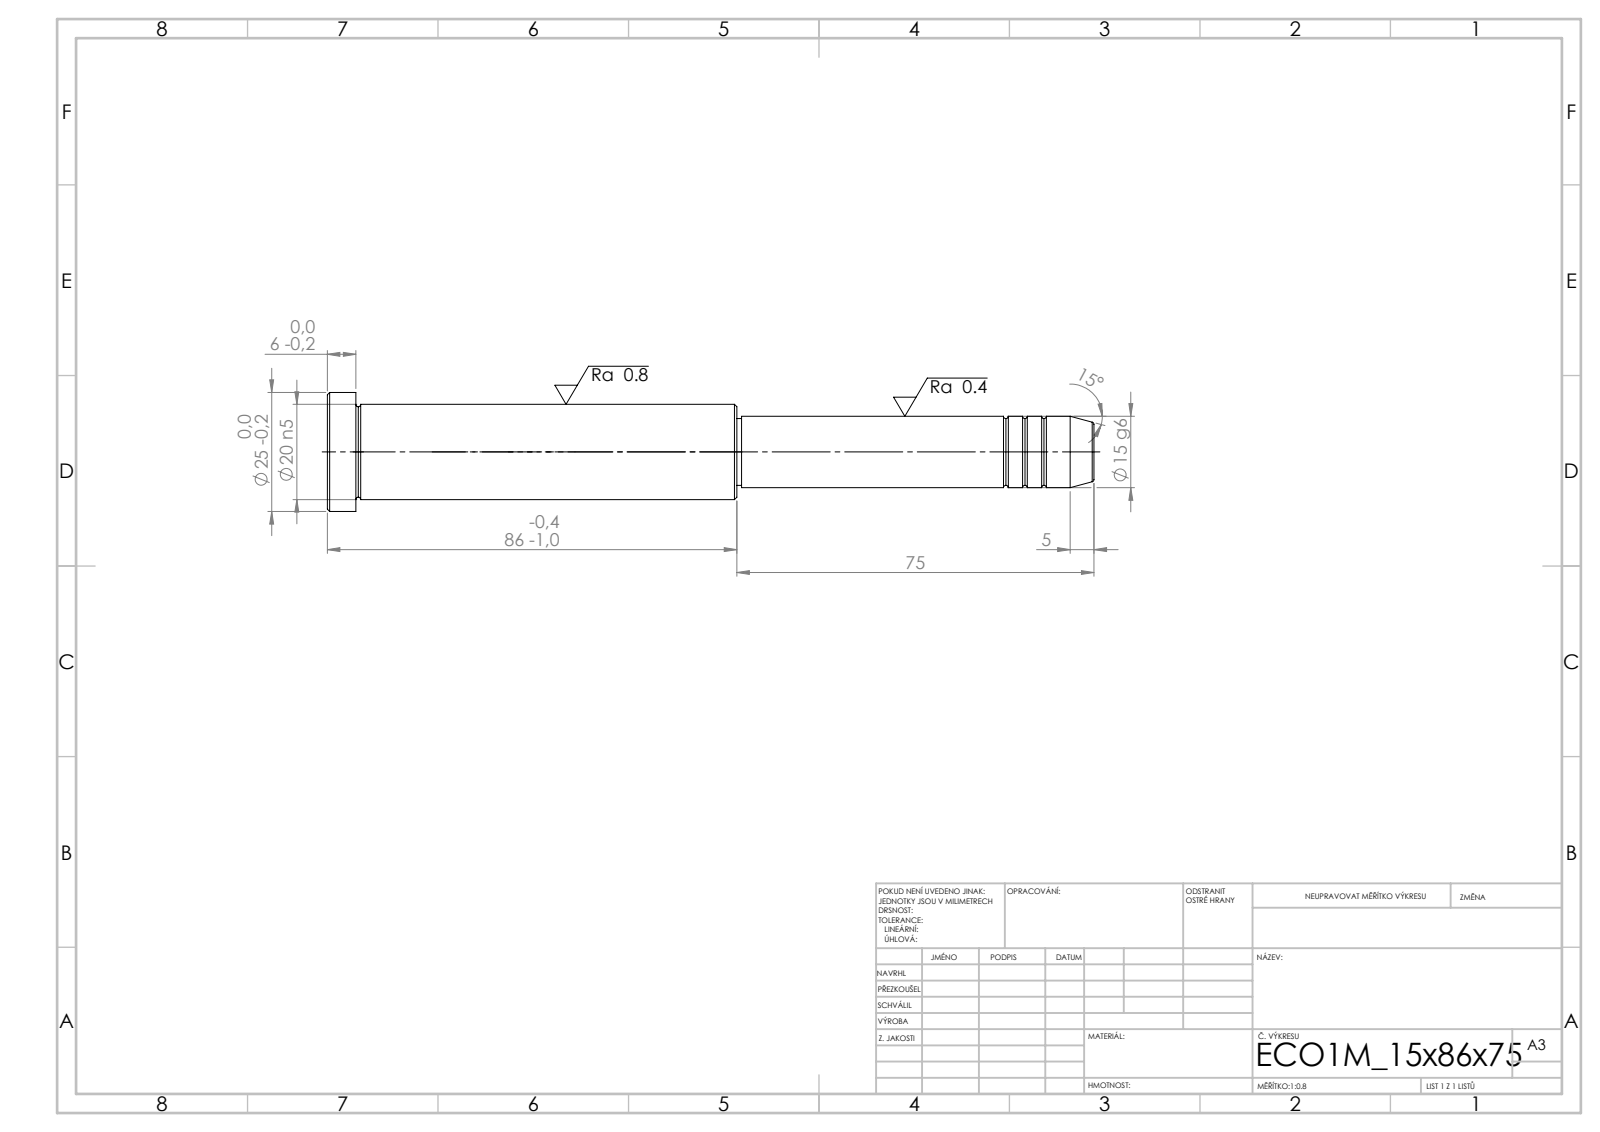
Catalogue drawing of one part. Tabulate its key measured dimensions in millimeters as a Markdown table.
| quantity | value |
| --- | --- |
| STEP written by | SolidWorks 2019 (CONFIG_CONTROL_DESIGN) |
| units | millimeters |
| bodies | 1 solid, 43 faces (5 planar, 14 cylindrical, 24 other) |
| overall size | 161 × 25 × 25 |
| volume | 41 064 mm³ |
| surface area | 10 043 mm² |
| round bosses / shafts (diameter × count) | 25 × 1, 20 × 1, 15 × 1, 14 × 1 |
| main face-to-face distances | 6, 80, 86, 75, 155, 161, 74, 1, 81, 87 |
